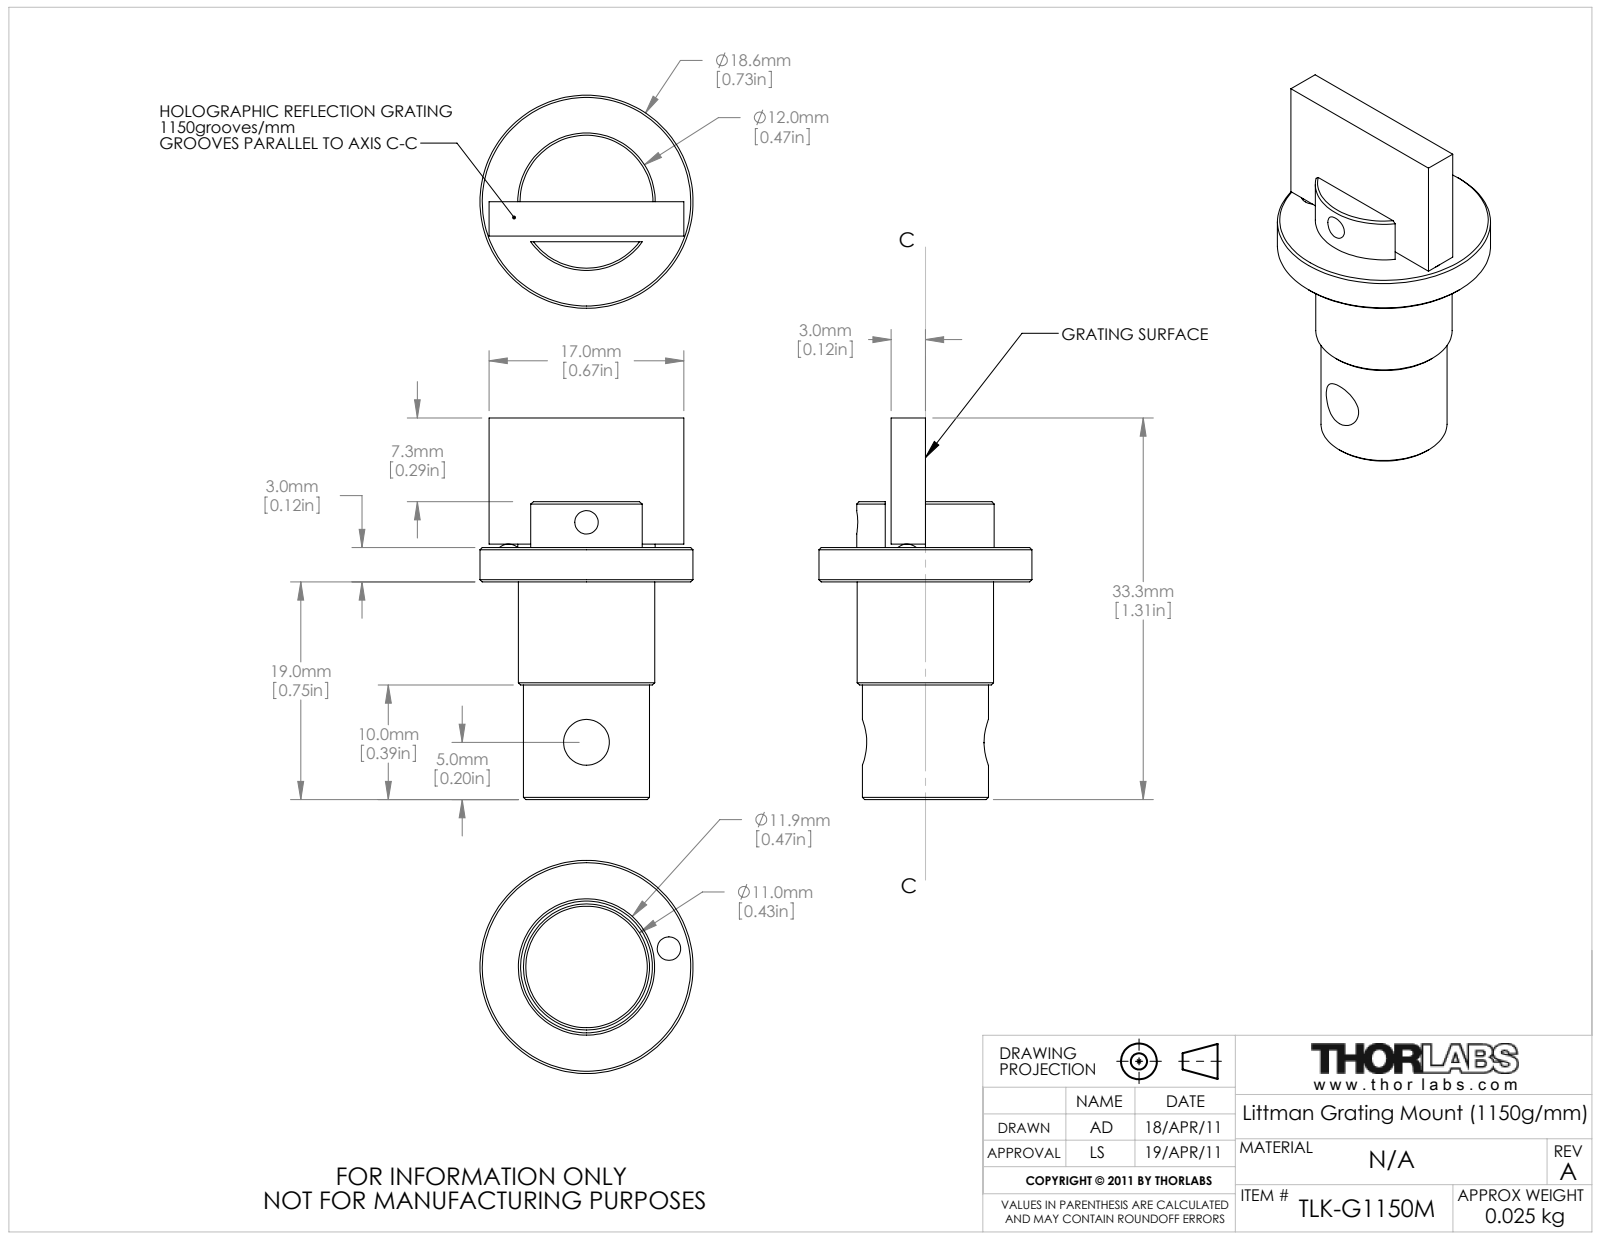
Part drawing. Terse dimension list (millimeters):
name: 21257-E0W
written by: SolidWorks 2011 (AUTOMOTIVE_DESIGN)
unit: mm
bodies: 3 solids, 45 faces (15 planar, 17 cylindrical, 13 other)
size: 33.3 × 18.6 × 18.6
volume: 3 461 mm³; area: 2 291 mm²
holes: 2× ⌀2.05, 1× ⌀2.6, 1× ⌀4
bosses: 1× ⌀18.6, 1× ⌀12, 1× ⌀11.9, 1× ⌀11
face distances: 3, 19, 22, 26, 7, 4, 22.3, 33.3, 3.3, 14.3
hole spacings: 14, 19.2
